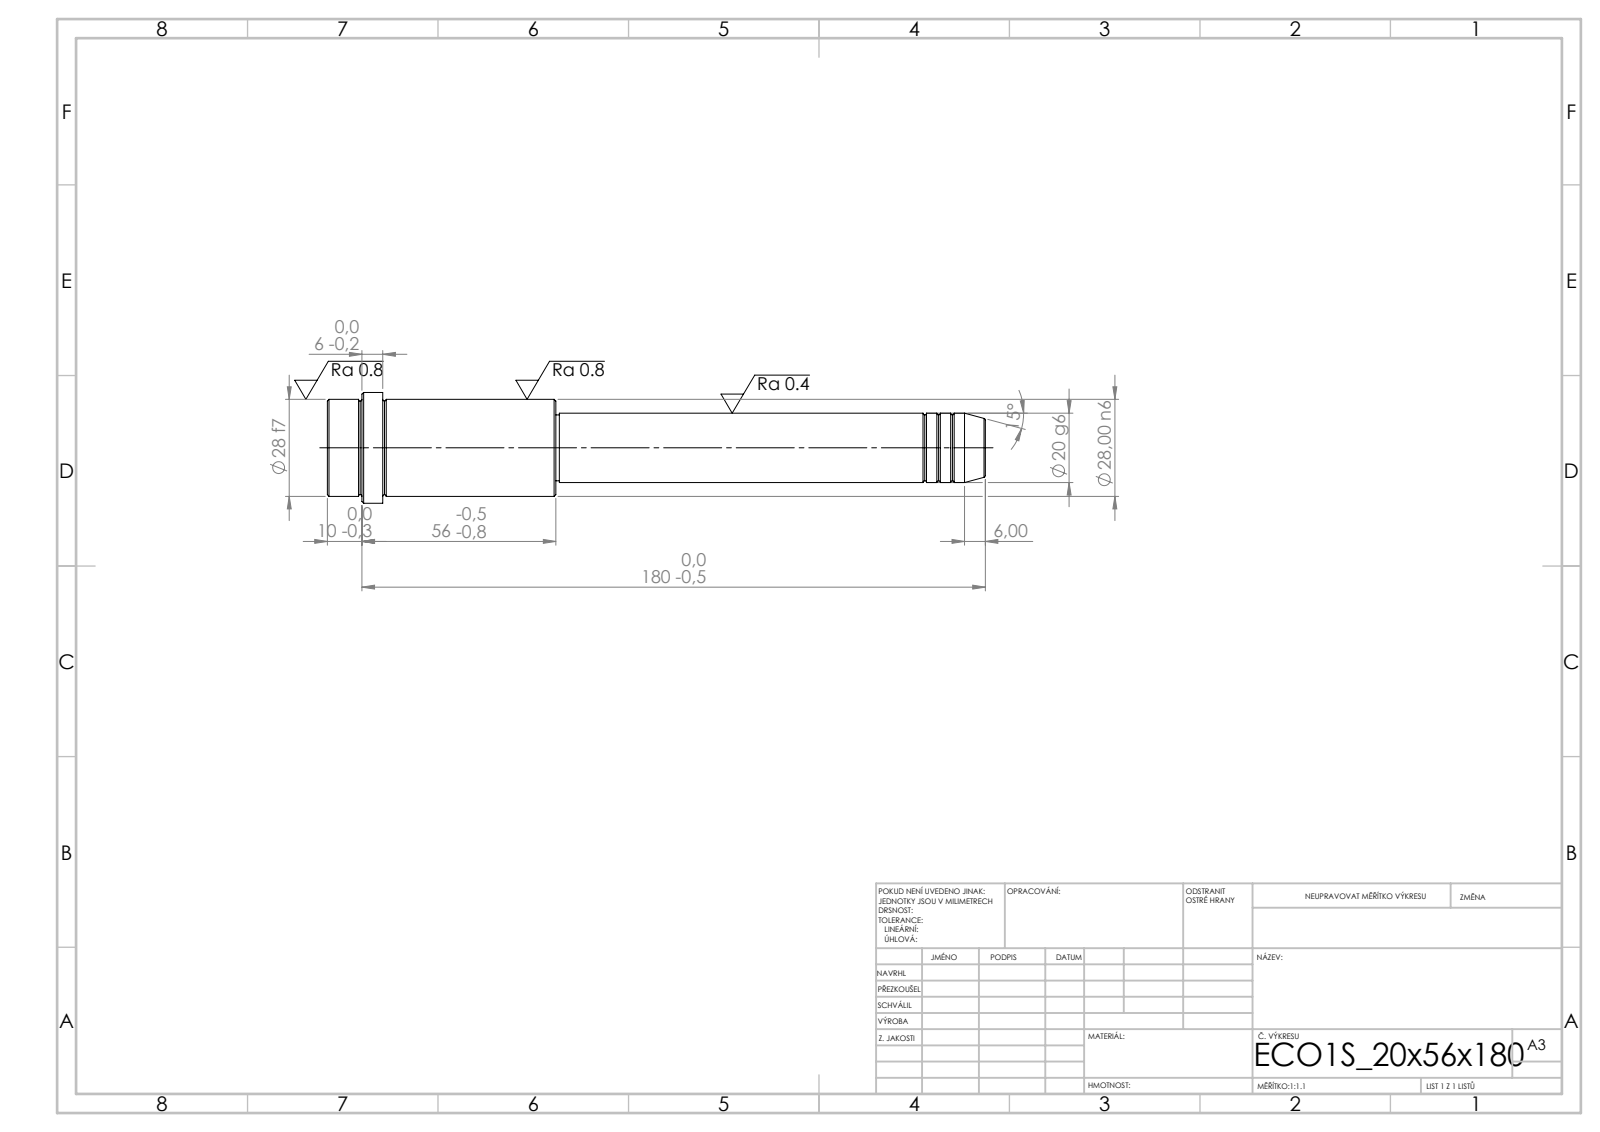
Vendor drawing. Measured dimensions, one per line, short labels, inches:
written by: SolidWorks 2019 (CONFIG_CONTROL_DESIGN)
unit: in
bodies: 1 solid, 52 faces (6 planar, 16 cylindrical, 30 other)
size: 7.48 × 1.26 × 1.26
volume: 4.896 in³; area: 23.76 in²
bosses: 1× ⌀1.26, 1× ⌀1.102, 1× ⌀0.787, 1× ⌀0.748
face distances: 2.598, 4.882, 7.48, 6.85, 1.969, 0.63, 7.087, 2.205, 0.236, 0.394
